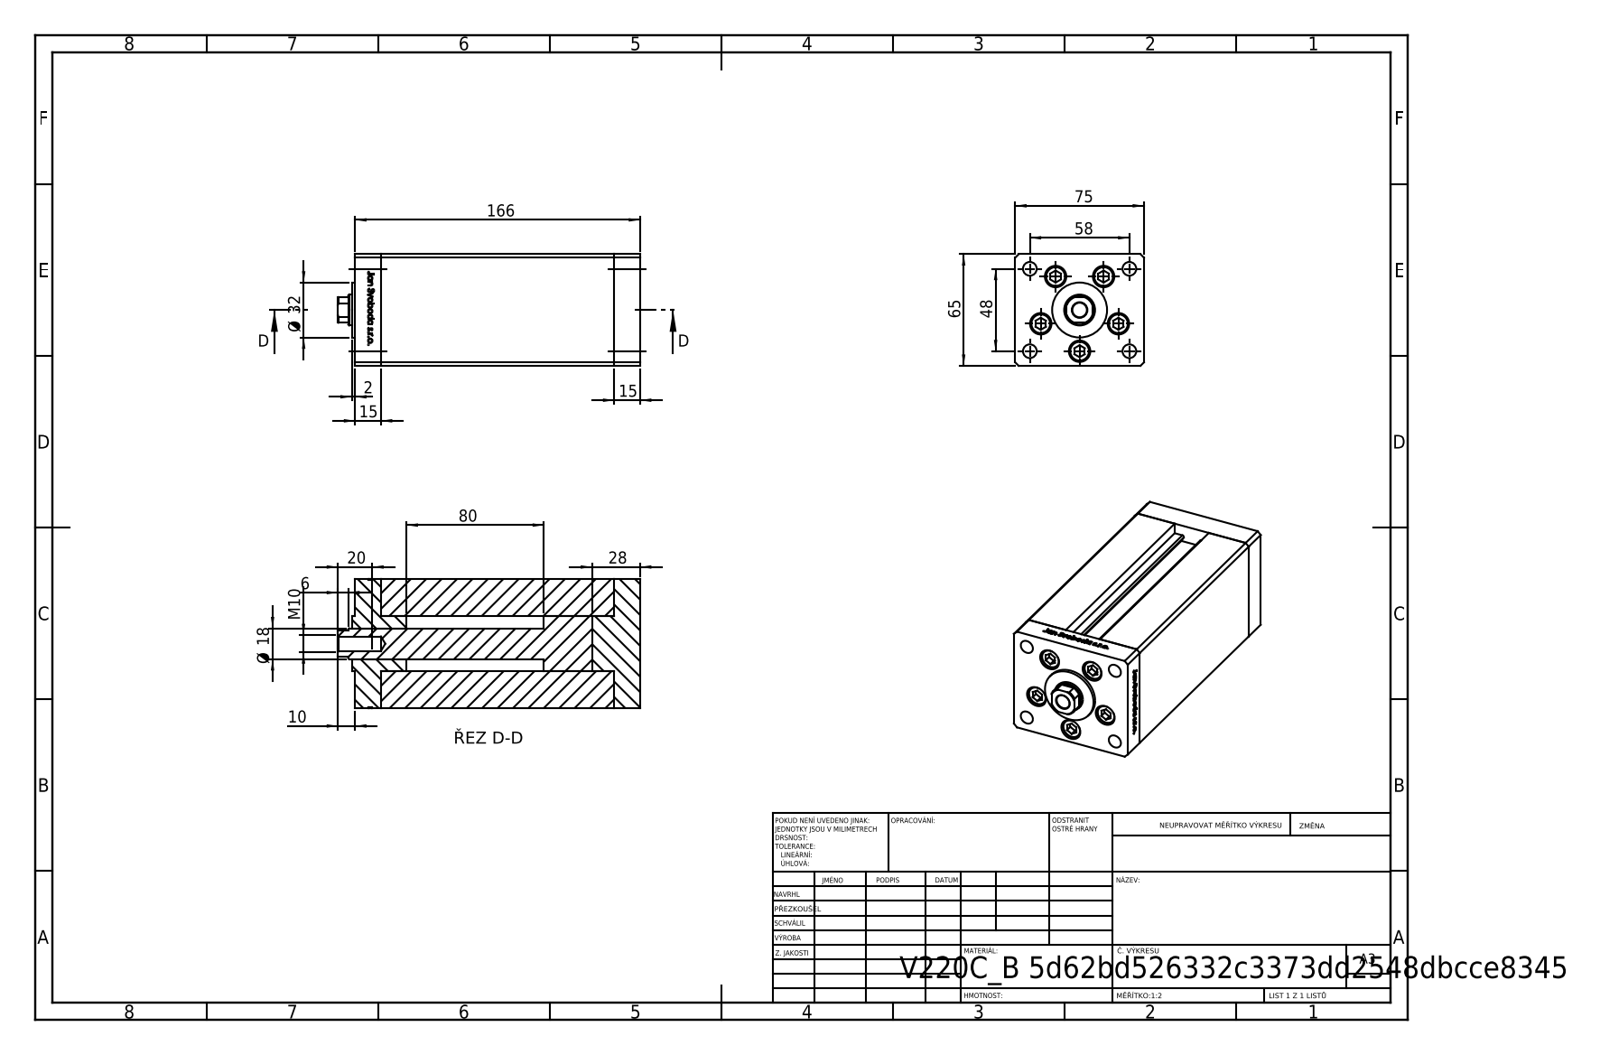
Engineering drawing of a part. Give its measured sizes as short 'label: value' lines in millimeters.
name: V220C_VC_B; V220C_FRONT_B; V220C_B MIDDLE; ALLEN BOLT (+1 more)
written by: SolidWorks 2019 (CONFIG_CONTROL_DESIGN)
unit: mm
bodies: 14 solids, 1183 faces (462 planar, 147 cylindrical, 574 other)
size: 176 × 75 × 65
volume: 722 498 mm³; area: 127 363 mm²
holes: 5× ⌀9, 5× ⌀12.5, 4× ⌀8, 2× ⌀2, 2× ⌀13.16, 1× ⌀8.5, 1× ⌀18
bosses: 5× ⌀8, 1× ⌀32
rounds: 2× R0.93, 1× R8.5
face distances: 75, 65, 15, 136, 151, 166, 28, 13, 54.5, 10.5
hole spacings: 24, 37.64, 15.67, 17.22, 27.71, 28.83, 29, 32.63
